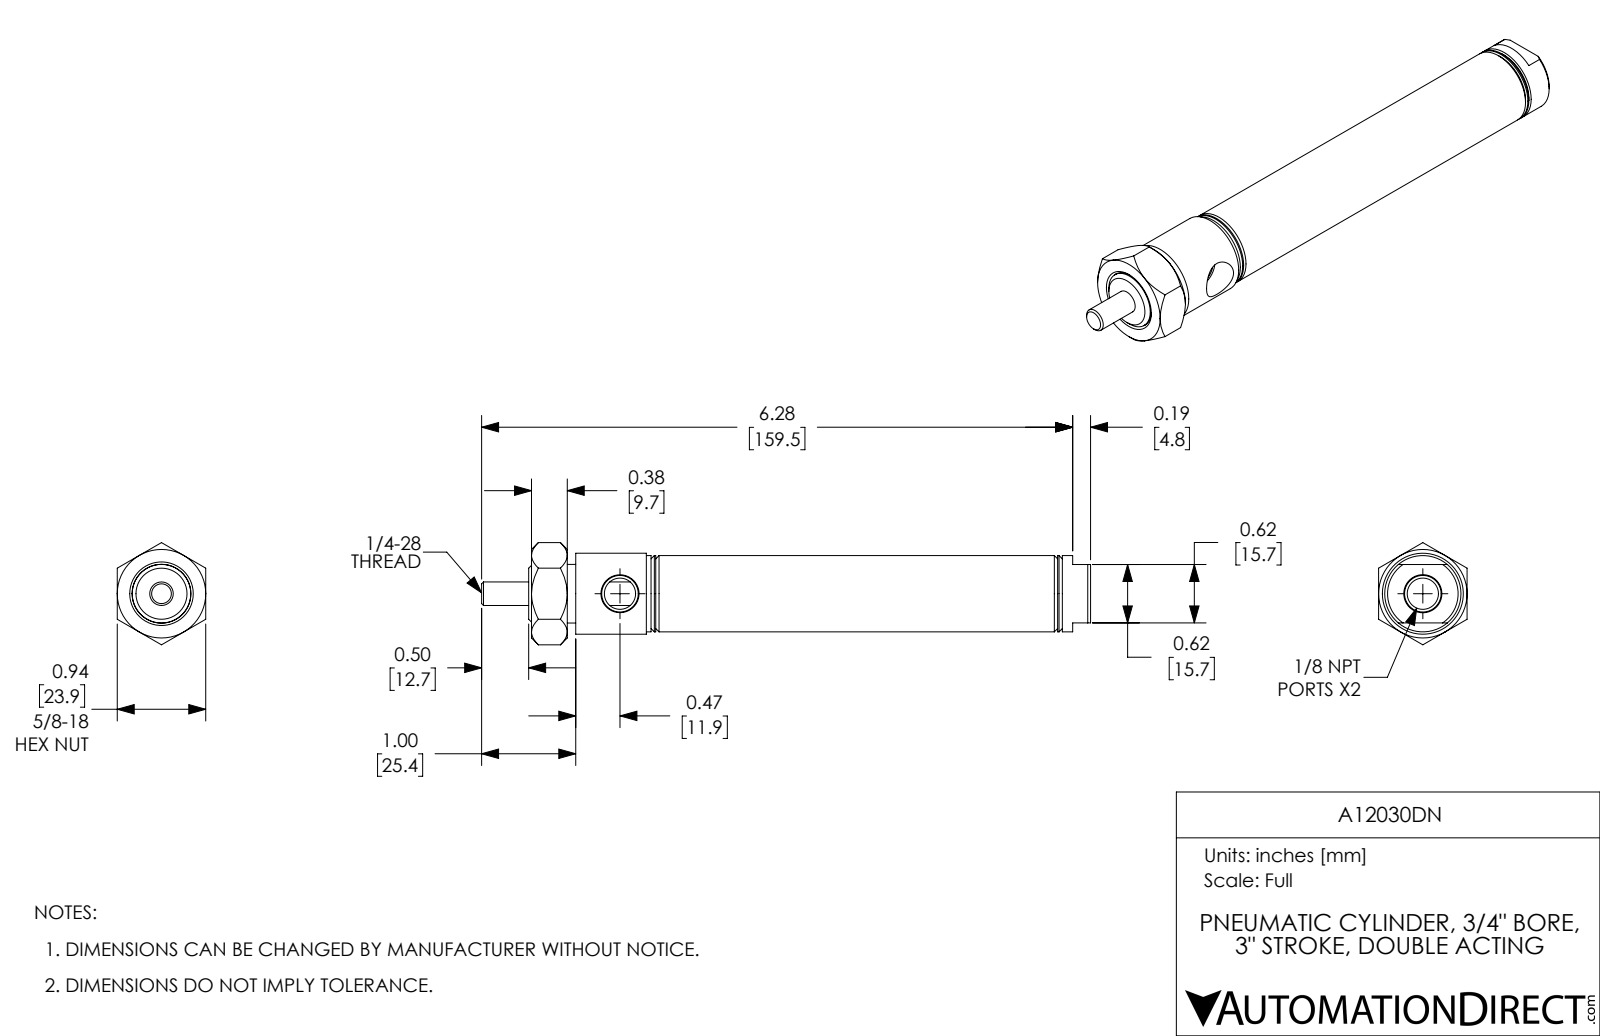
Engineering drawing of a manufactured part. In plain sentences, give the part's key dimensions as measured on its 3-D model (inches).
The part is named "A12030DN_Mounting Nut_D-9; A12030DN-Rod; A12030DN; A12030DN-MainBody". Its 3-D file was written by "SolidWorks 2017 (AUTOMOTIVE_DESIGN)". It is 3 solids with 94 faces: 27 planar, 28 cylindrical and 39 other. Overall it measures 6.47 by 1.085 by 0.94 inches. Its volume is 1.881 cubic inches and its surface area 36.58 square inches. Round holes: 2 of diameter 0.332, 1 of diameter 0.25, 1 of diameter 0.625, 1 of diameter 0.75. Round bosses or shafts: 1 of diameter 0.86, 1 of diameter 0.81, 1 of diameter 0.623. The main face-to-face distances are 4.485, 0.94, 0.5, 0.985, 1.485, 3.5, 3, 4.575, 4.075, 1.075.
